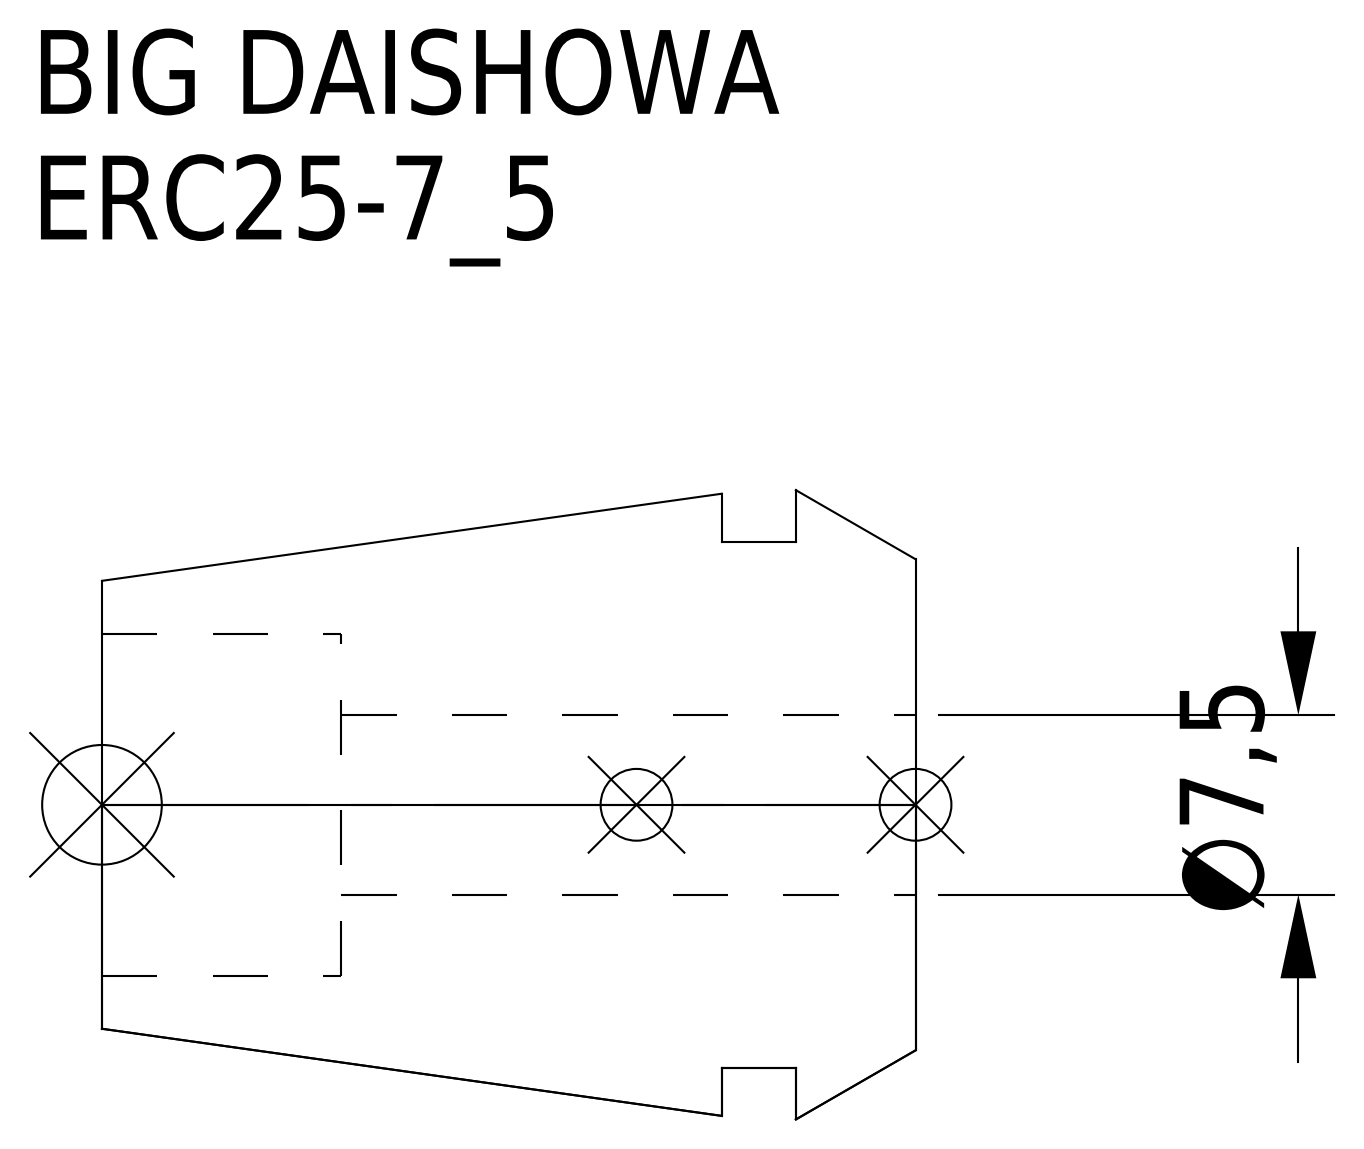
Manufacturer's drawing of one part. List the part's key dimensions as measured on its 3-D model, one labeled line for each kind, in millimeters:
Part name (STEP PRODUCT): ERC25-7_5
STEP written by: CREO PARAMETRIC BY PTC INC, 2016380 (AUTOMOTIVE_DESIGN)
Units: millimetres
Bodies: 1 solid, 15 faces (5 planar, 6 cylindrical, 4 other)
Overall size (bounding box): 34 × 26.3 × 26.3
Volume: 10 936 mm³ · Surface area: 4 323 mm²
Round holes (diameter × count): ⌀7.5 ×1, ⌀14.3 ×1
Round bosses / shafts (diameter × count): ⌀22 ×1
Main face-to-face distances: 5, 8.1, 3.1, 24, 19, 15.9, 34, 29, 25.9, 10
